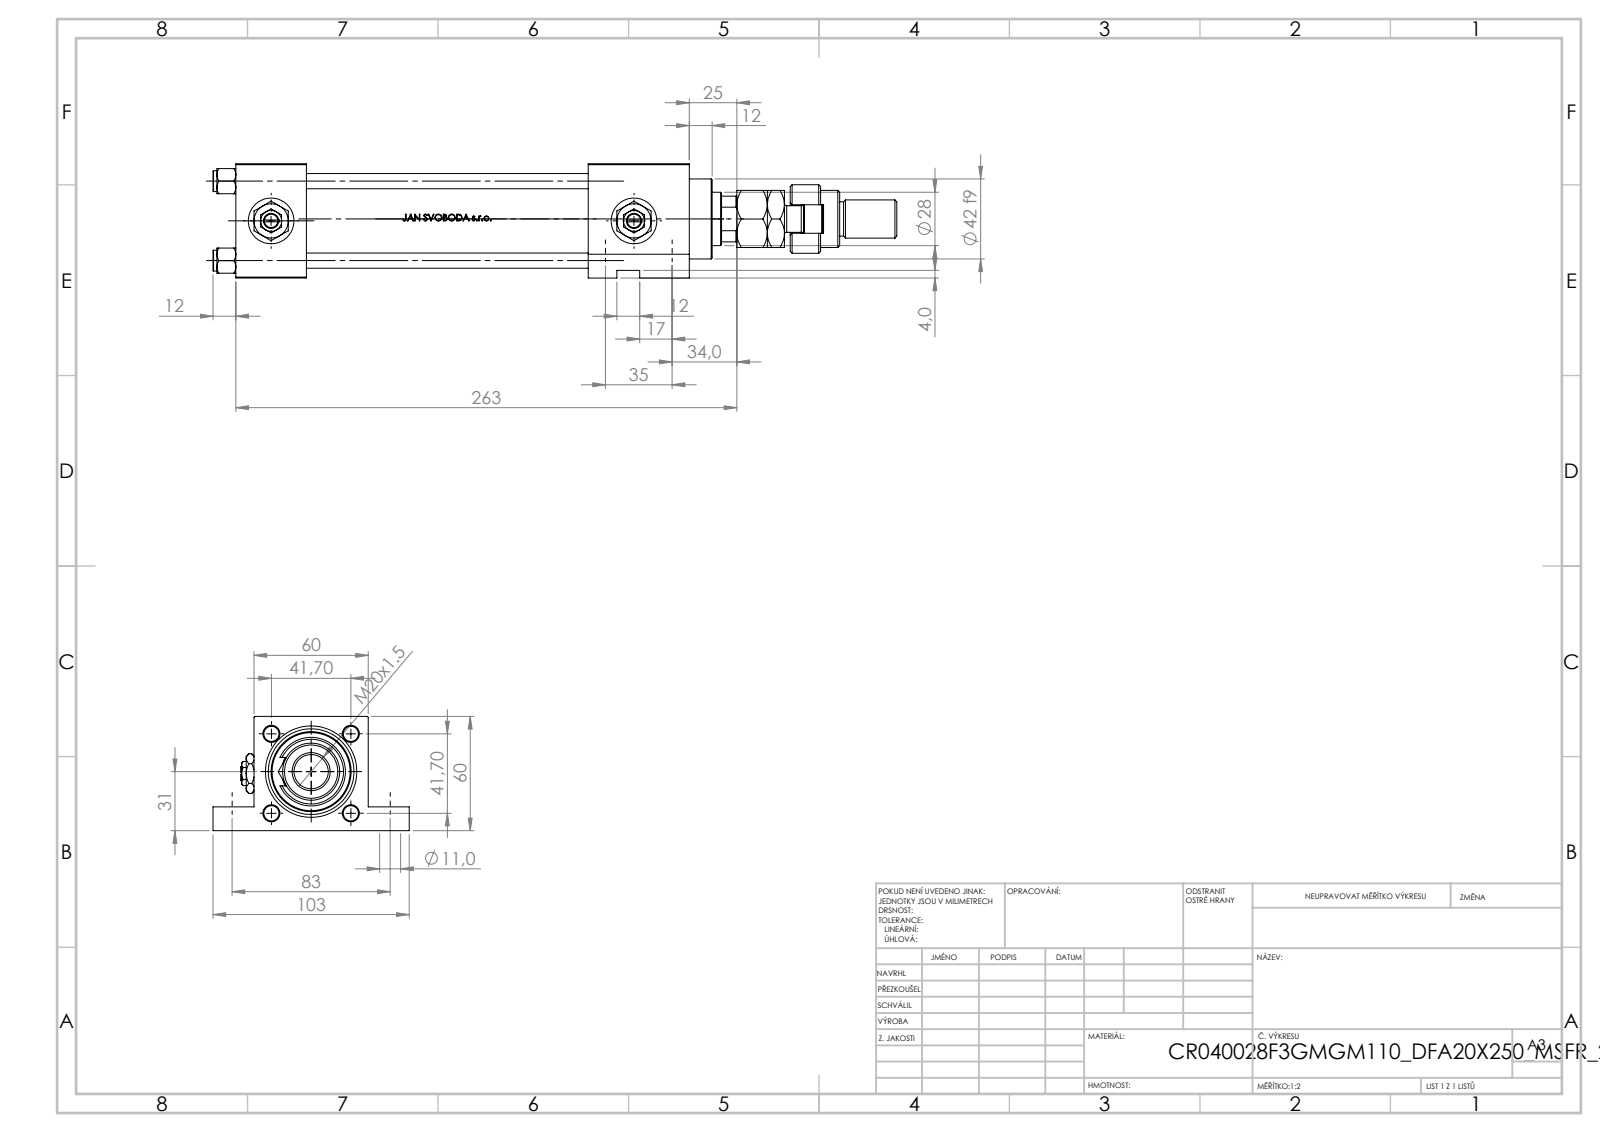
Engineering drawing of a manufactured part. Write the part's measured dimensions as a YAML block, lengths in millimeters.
part_name: "V215CR_F_TYCINKA; Zatka_pro_OIL_PORT; MFA; V215CR_F_Body (+4 more)"
step_written_by: "SolidWorks 2019 (CONFIG_CONTROL_DESIGN)"
units: millimeters
bodies: {solids: 15, faces: 1301, planar: 514, cylindrical: 161, other: 626}
overall_size: [359, 103, 60]
volume: 600596
surface_area: 175206
round_holes:
  - {diameter: 8, count: 4}
  - {diameter: 11, count: 4}
  - {diameter: 16.66, count: 3}
  - {diameter: 24, count: 3}
  - {diameter: 2.5, count: 2}
  - {diameter: 7, count: 2}
  - {diameter: 16, count: 1}
  - {diameter: 18.5, count: 1}
  - {diameter: 28, count: 1}
  - {diameter: 31, count: 1}
  - {diameter: 40, count: 1}
  - {diameter: 45, count: 1}
round_bosses_or_shafts:
  - {diameter: 11, count: 4}
  - {diameter: 46, count: 1}
  - {diameter: 42, count: 1}
  - {diameter: 36, count: 1}
  - {diameter: 30, count: 1}
  - {diameter: 22, count: 1}
  - {diameter: 20, count: 1}
  - {diameter: 18, count: 1}
partial_cylinders:
  - {radius: 7.5, count: 1}
  - {radius: 12, count: 1}
  - {radius: 13.5, count: 1}
face_to_face_distances: [60, 37, 53, 185, 148, 238, 38, 201, 15, 12.5]
hole_center_spacings: [20.85, 29.49, 41.7, 46.53, 20.75, 35, 58.97, 83]
